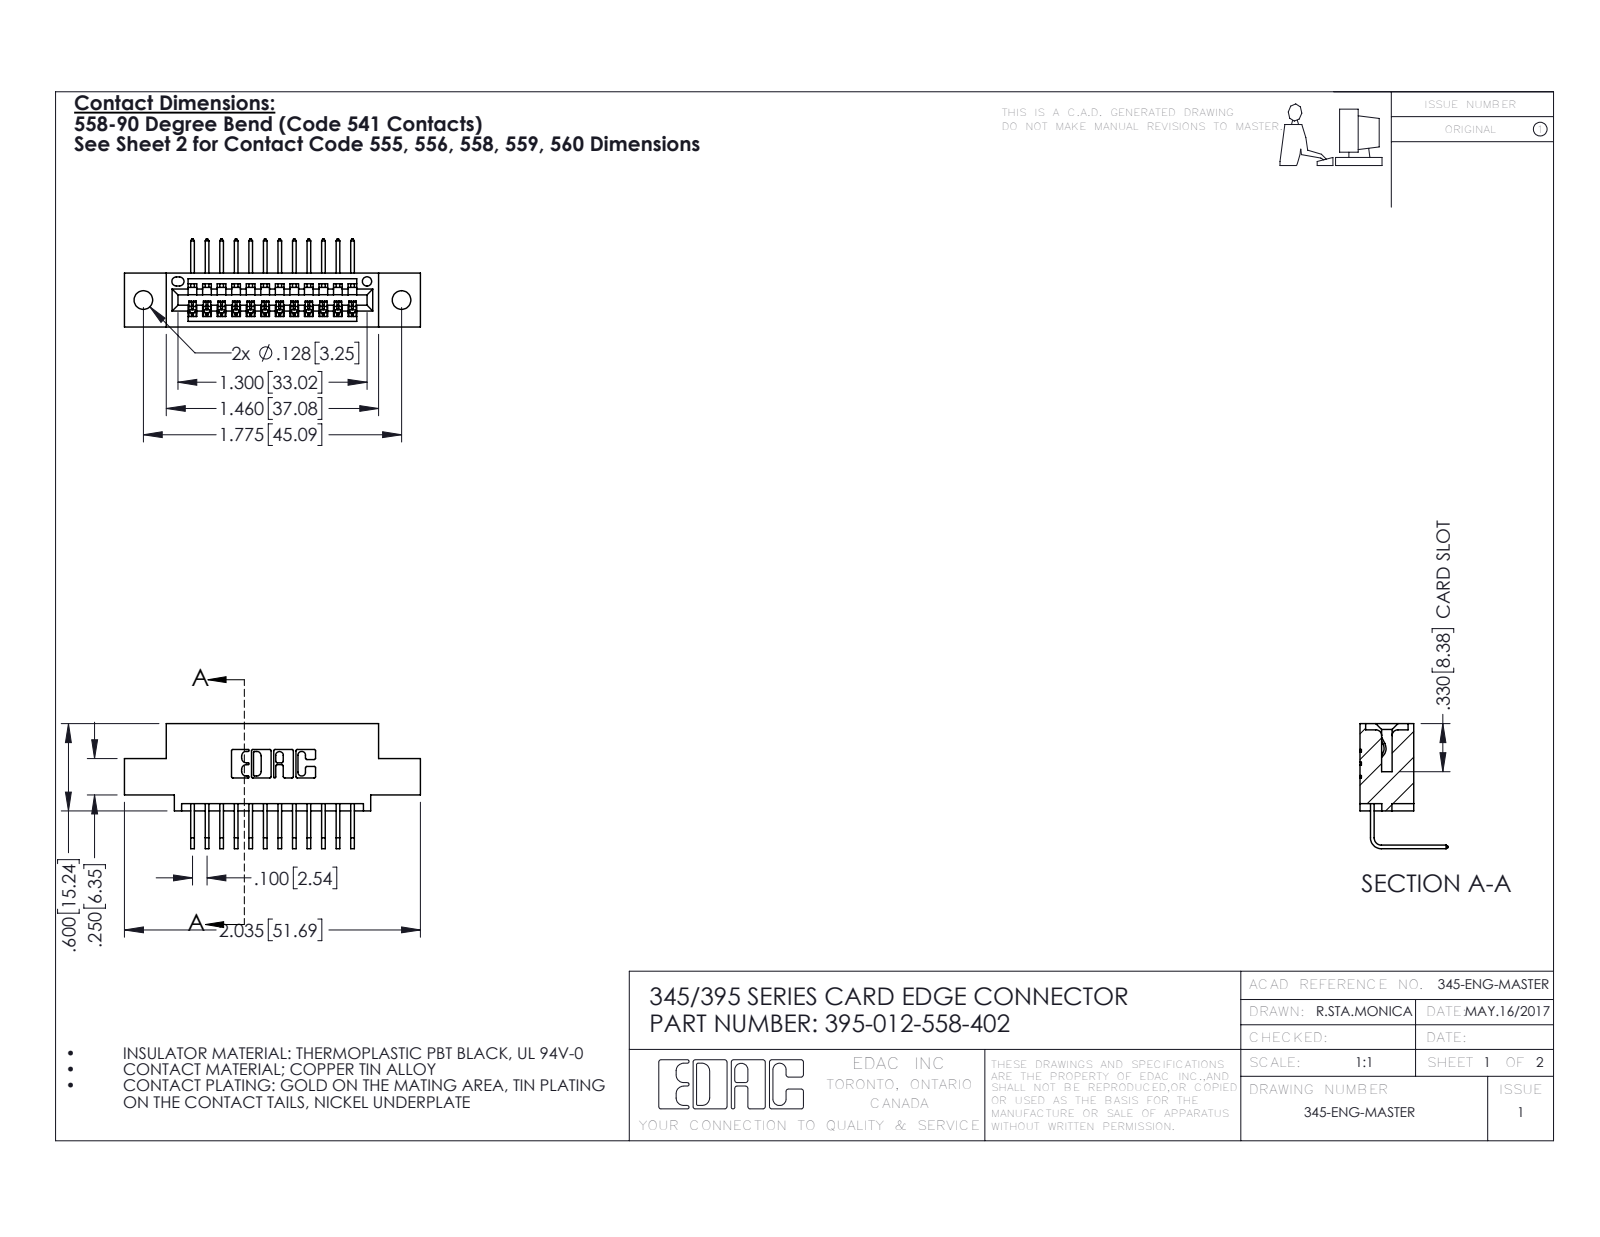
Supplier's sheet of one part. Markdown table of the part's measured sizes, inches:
| quantity | value |
| --- | --- |
| part name | 395-012-558-402; 345 Part_0.110 Offset - 0.128 Dia; 345-292-001_558 Tail - 2 |
| STEP written by | SolidWorks 2016 (CONFIG_CONTROL_DESIGN) |
| units | inches |
| bodies | 13 solids, 850 faces (588 planar, 262 cylindrical, 0 other) |
| overall size | 2.035 × 0.859 × 0.605 |
| volume | 0.28 in³ |
| surface area | 8.9 in² |
| round holes (diameter × count) | 0.128 × 2, 0.064 × 1 |
| partial cylindrical surfaces (radius × count) | 0.006 × 24, 0.01 × 22, 0.007 × 6, 0.031 × 6, 0.026 × 3, 0.031 × 2, 0.04 × 2, 0.014 × 1 |
| main face-to-face distances | 0.072, 0.298, 0.2, 0.37, 0.098, 0.272, 0.025, 0.1, 0.16, 0.3 |
| hole center spacings | 0.27, 1.543, 1.775 |
